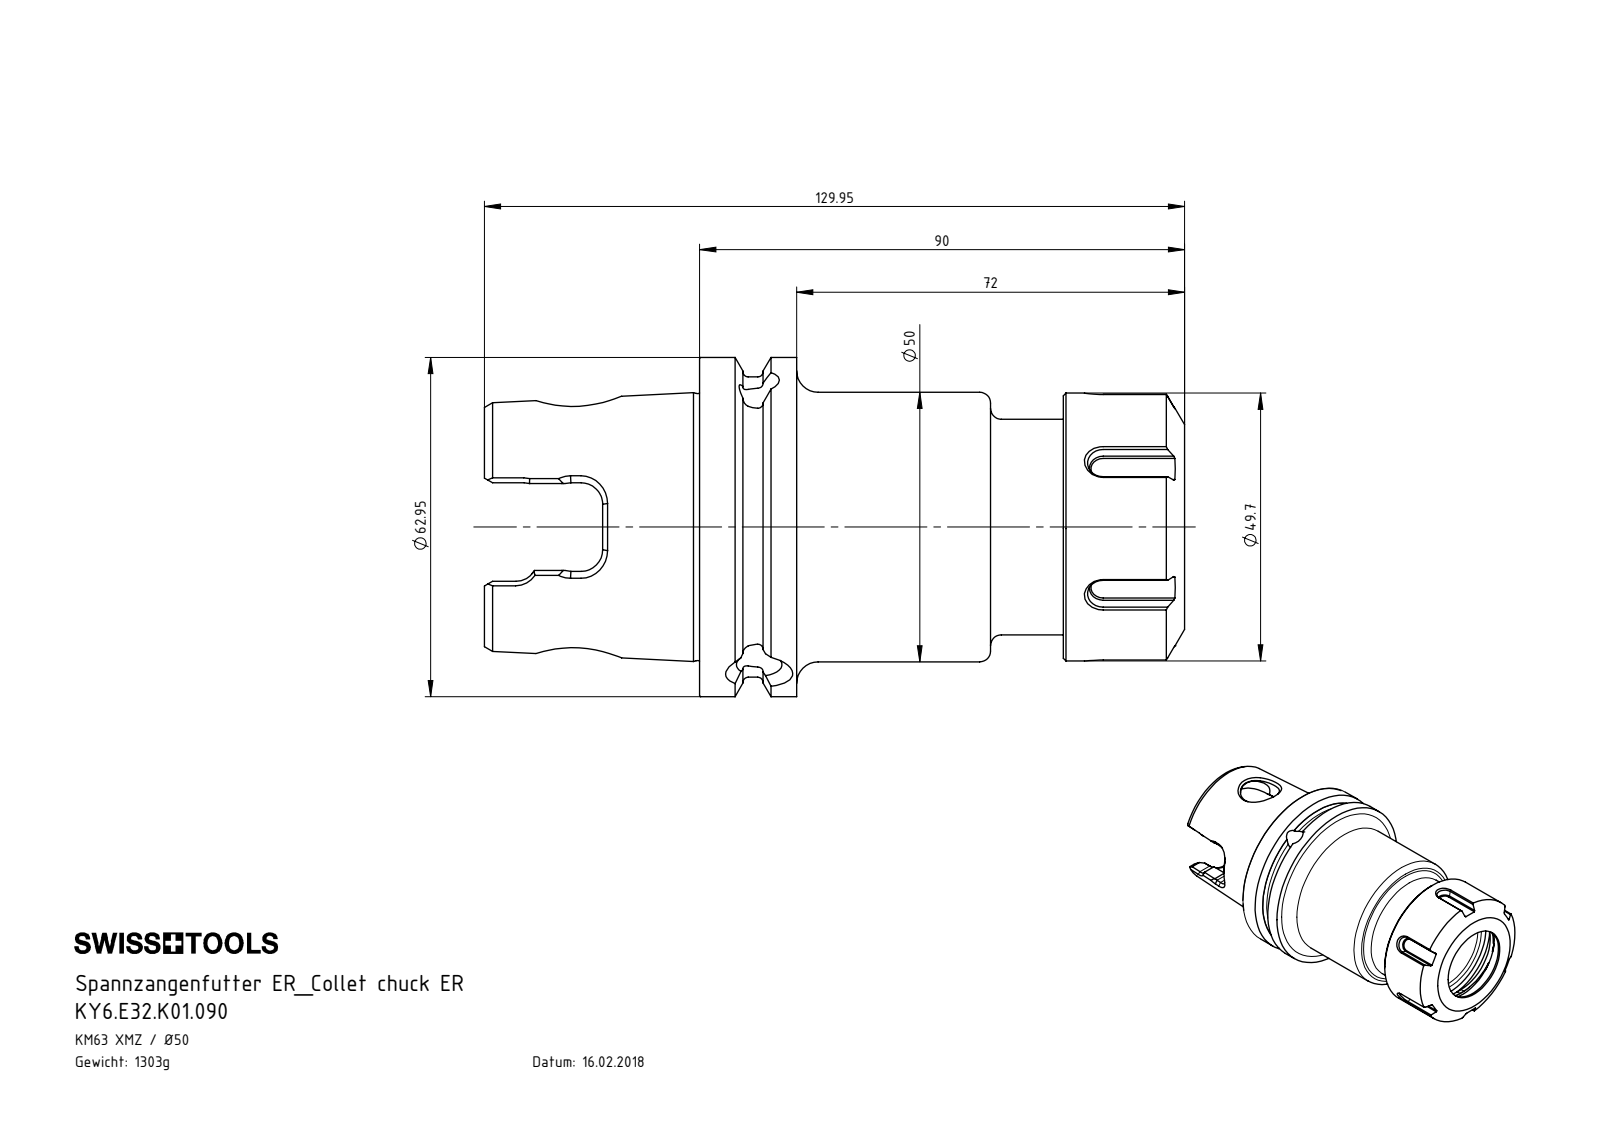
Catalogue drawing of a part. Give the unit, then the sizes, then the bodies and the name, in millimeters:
Units: millimetres
Overall size (bounding box): 129.95 × 62.95 × 62.95
Round holes (diameter × count): ⌀7.47 ×2, ⌀8 ×1, ⌀8.48 ×1, ⌀10 ×1, ⌀11.5 ×1, ⌀14.5 ×1, ⌀20.5 ×1, ⌀24 ×1, ⌀27.1 ×1, ⌀31.1 ×1, ⌀35.27 ×1, ⌀36.5 ×1
Round bosses / shafts (diameter × count): ⌀62.95 ×1, ⌀55.7 ×1, ⌀50 ×1, ⌀49.7 ×1, ⌀40 ×1
Partial cylindrical surfaces — rounded edges, fillets, slot ends (radius × count): R4 ×6, R7.04 ×2, R15.5 ×2
Main face-to-face distances: 67.5, 1.1, 68.6, 91.1, 90, 22.5, 18, 72, 19.1, 49.5
Volume: 166 015 mm³ · Surface area: 41 006 mm²
Bodies: 2 solids, 324 faces (100 planar, 68 cylindrical, 156 other)
Part name (STEP PRODUCT): E32-ER1.001.022; KY6-E32.K01.090_C; KY6.E32.K01.090
STEP written by: SolidWorks 2017 (CONFIG_CONTROL_DESIGN)
